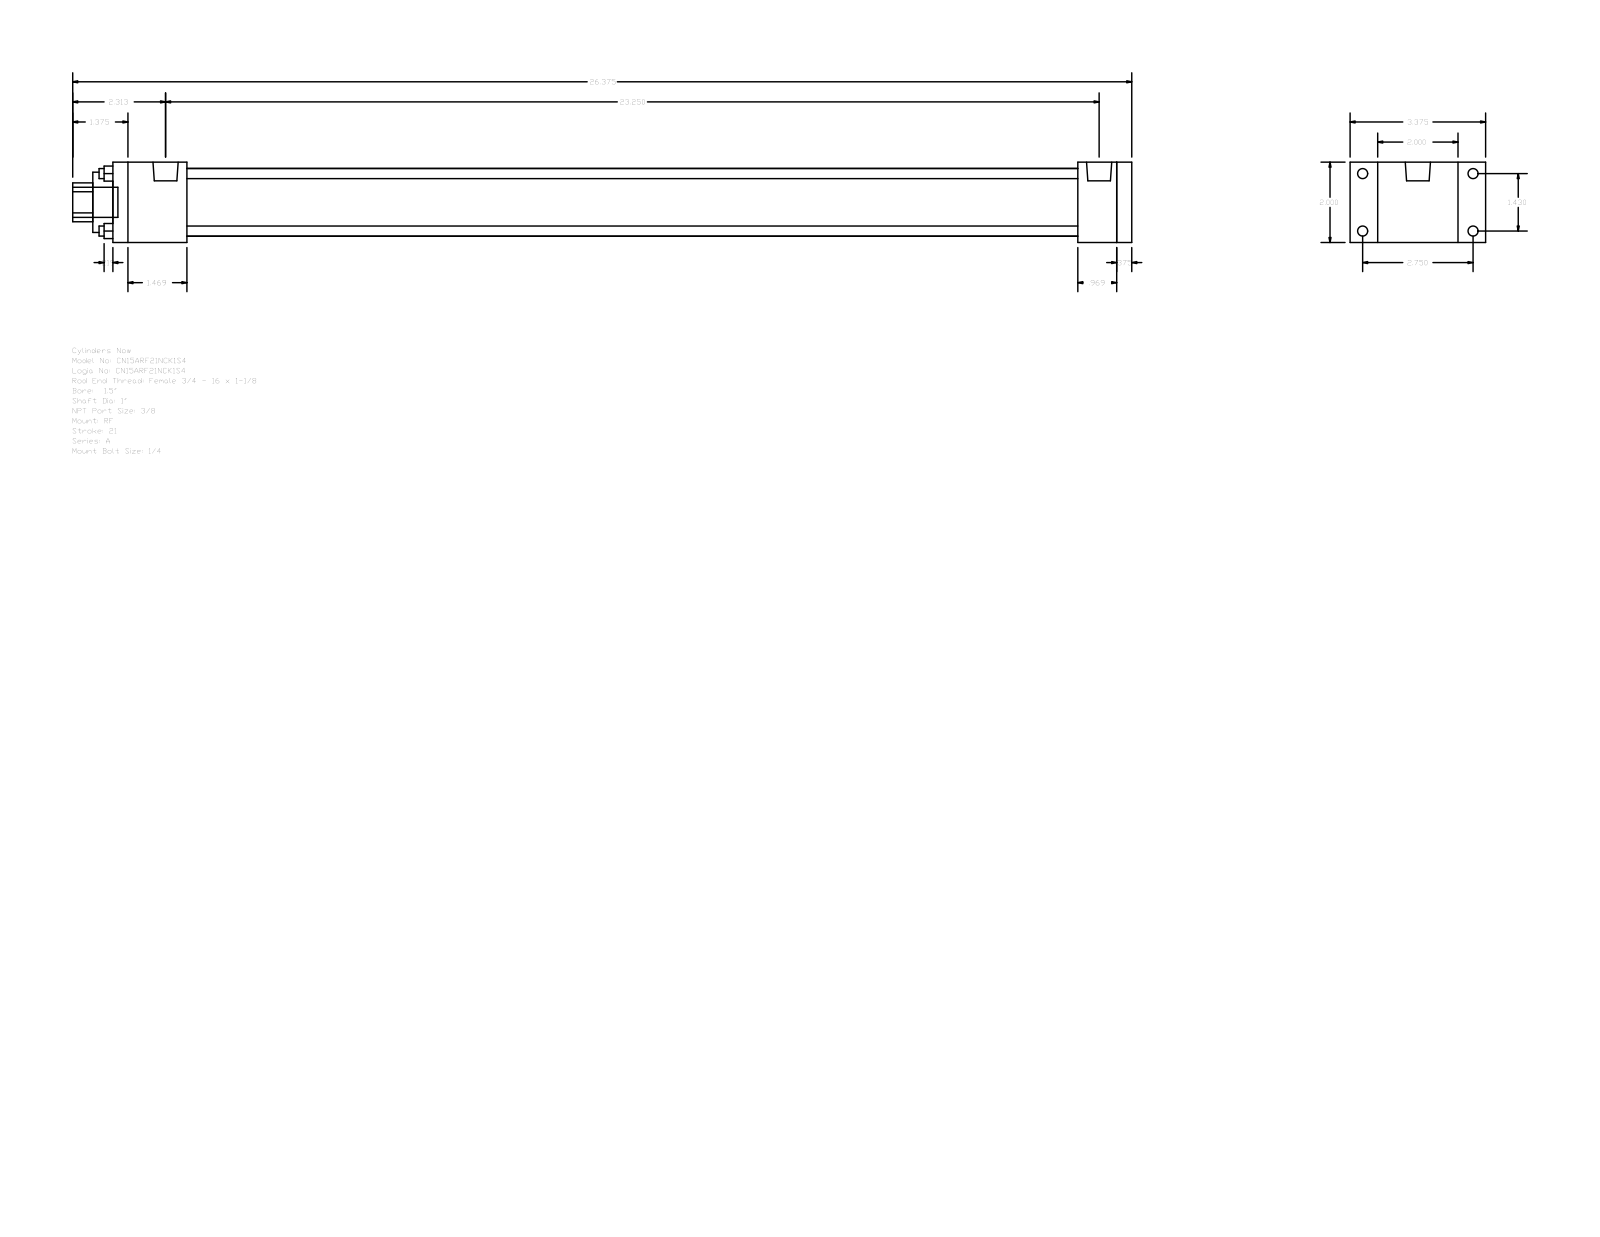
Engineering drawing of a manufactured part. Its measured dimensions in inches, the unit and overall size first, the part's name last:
Units: inches
Overall size (bounding box): 26.375 × 3.375 × 2
Round holes (diameter × count): ⌀0.25 ×4, ⌀1 ×1, ⌀1.5 ×1, ⌀1.69 ×1
Round bosses / shafts (diameter × count): ⌀0.25 ×4, ⌀0.219 ×4, ⌀0.627 ×2, ⌀0.75 ×1
Partial cylindrical surfaces — rounded edges, fillets, slot ends (radius × count): R0.484 ×1
Main face-to-face distances: 2, 0.375, 25, 25.375, 24.031, 0.969, 1.344, 1.844, 22.187, 23.156
Hole centre spacings: 1.011, 1.43, 2.022
Bodies: 0 solids, 92 faces (64 planar, 28 cylindrical, 0 other)
Part name (STEP PRODUCT): A_RF__0150_1
STEP written by: GSSL Pune (CONFIG_CONTROL_DESIGN)
